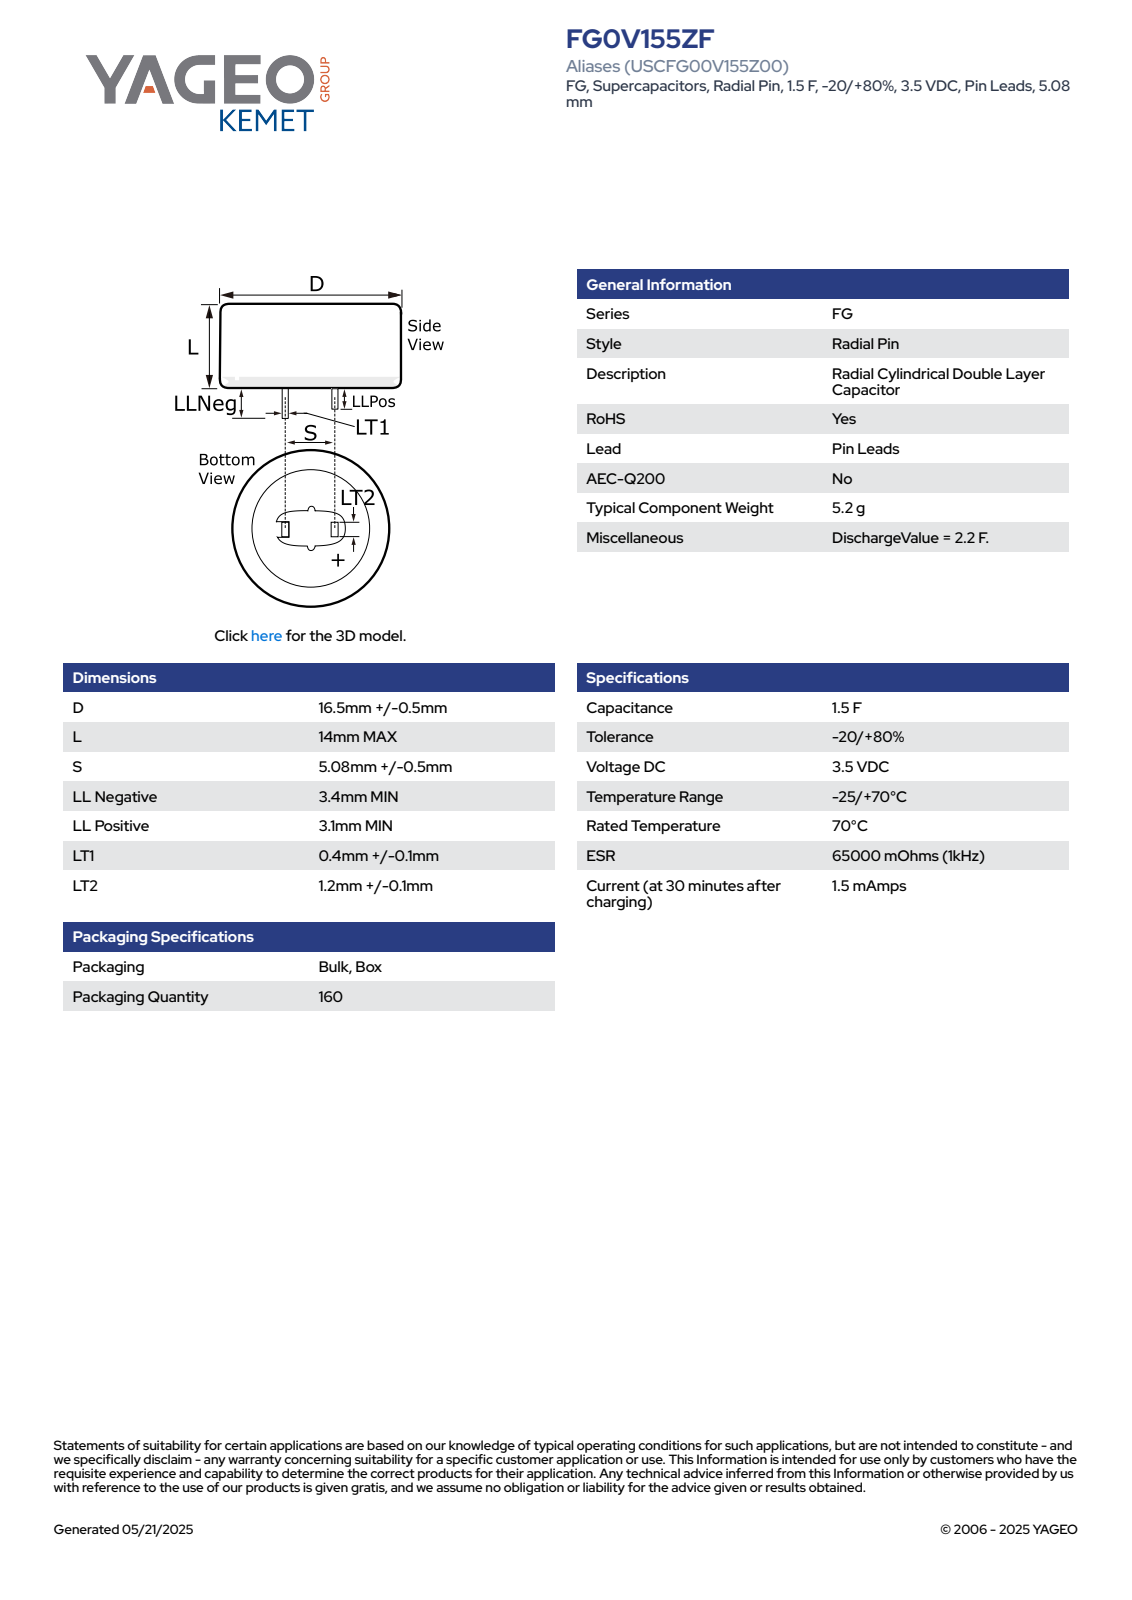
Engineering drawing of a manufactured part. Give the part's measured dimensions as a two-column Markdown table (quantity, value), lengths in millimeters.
| quantity | value |
| --- | --- |
| part name | CDR_LPLLN_D17L14S5.08LLNEG3.4LLPOS3.1LT10.5LT21.3 |
| STEP written by | SolidWorks 2014 (AUTOMOTIVE_DESIGN) |
| units | millimeters |
| bodies | 1 solid, 78 faces (70 planar, 4 cylindrical, 4 other) |
| overall size | 17.4 × 17 × 17 |
| volume | 3 164 mm³ |
| surface area | 1 184 mm² |
| round bosses / shafts (diameter × count) | 17 × 1 |
| partial cylindrical surfaces (radius × count) | 8.51 × 1 |
| main face-to-face distances | 14, 0.5, 5.08, 5.58, 4.58, 1.3, 3.4, 17.4, 3.1, 17.1 |
